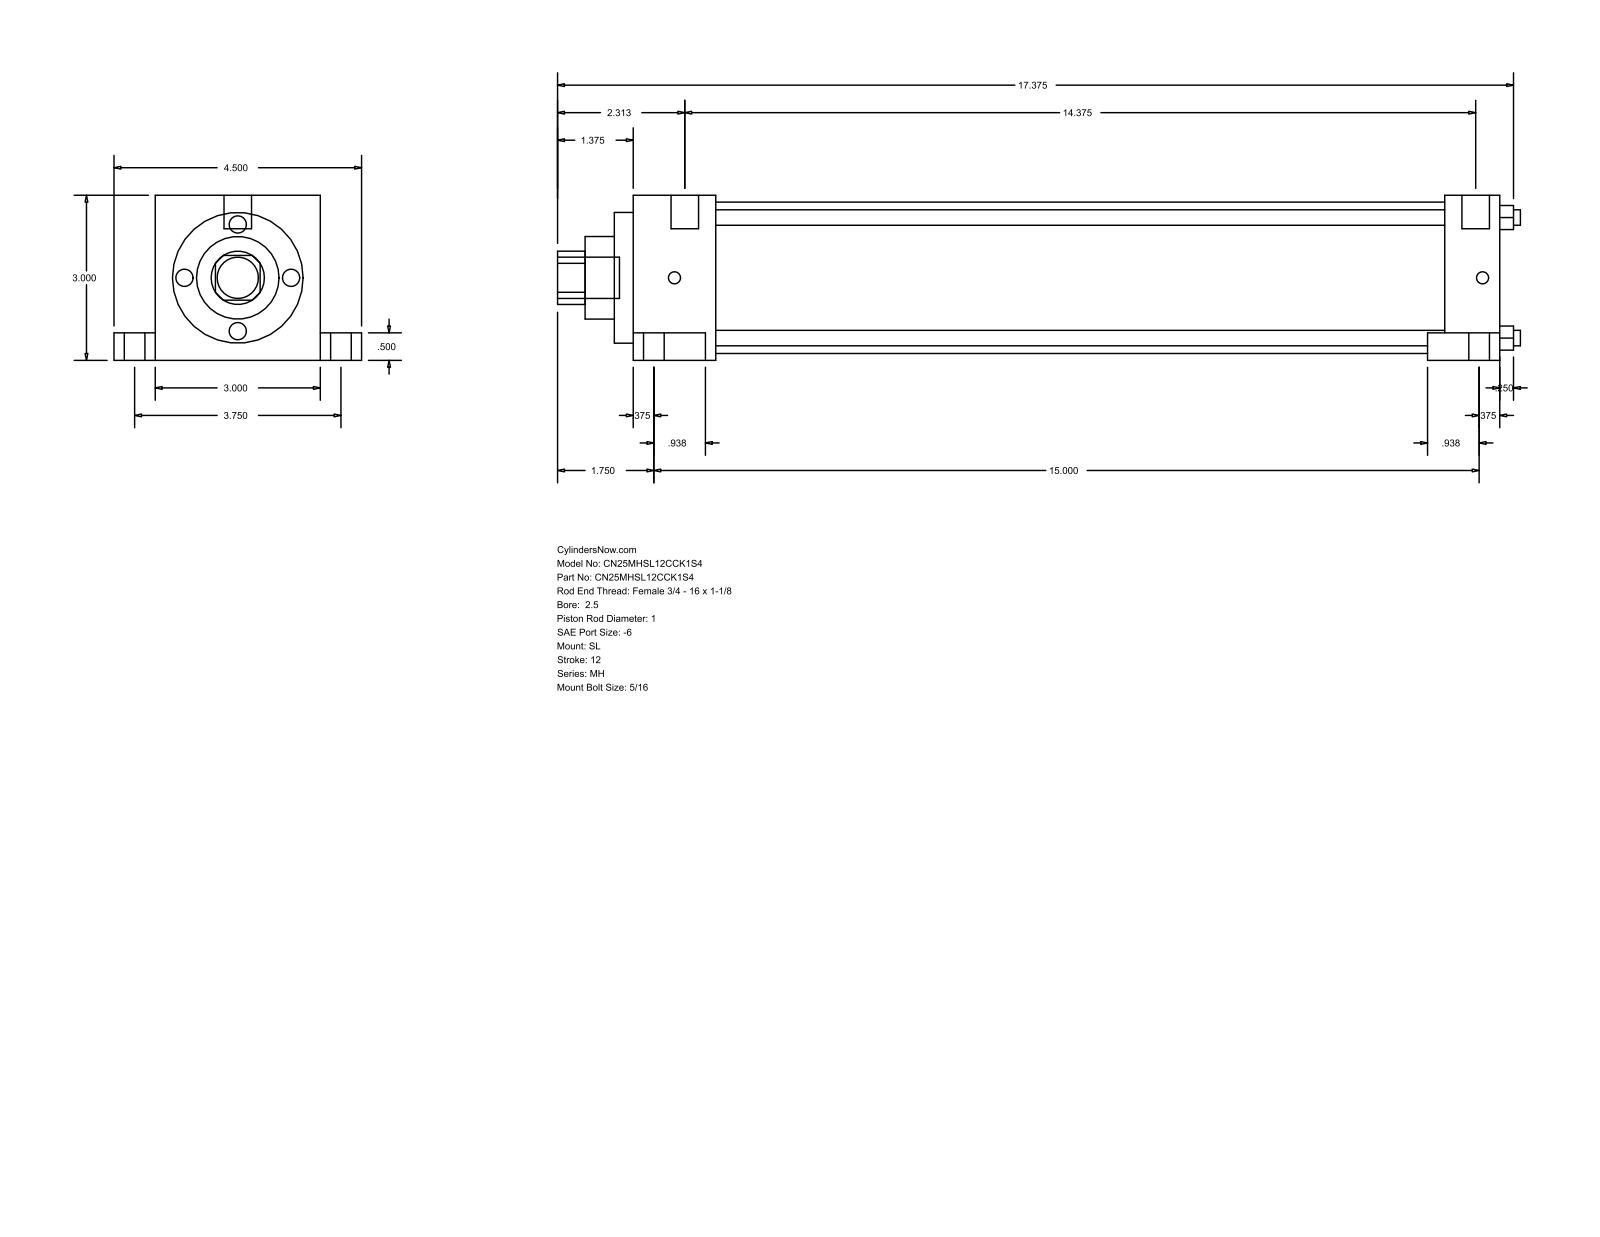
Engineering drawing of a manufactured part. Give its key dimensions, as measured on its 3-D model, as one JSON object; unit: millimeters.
{"part_name": "MH_SL__0250_1", "step_written_by": "GSSL Pune (CONFIG_CONTROL_DESIGN)", "units": "millimeters", "bodies": {"solids": 0, "faces": 86, "planar": 61, "cylindrical": 25, "other": 0}, "overall_size": [444.5, 114.3, 76.2], "round_holes": [[7.14, 4], [25.4, 1], [38.1, 1], [60.33, 1], [69.85, 1]], "round_bosses_or_shafts": [[15.88, 2], [9.53, 2], [5.56, 2], [19.05, 1], [12.7, 1]], "partial_cylinders_radius": [[12.29, 1]], "face_to_face_distances": [76.2, 25.41, 383.38, 408.79, 12.7, 63.5, 19.05, 95.25, 13.49, 396.87], "hole_center_spacings": [39.33, 55.62, 78.66]}
